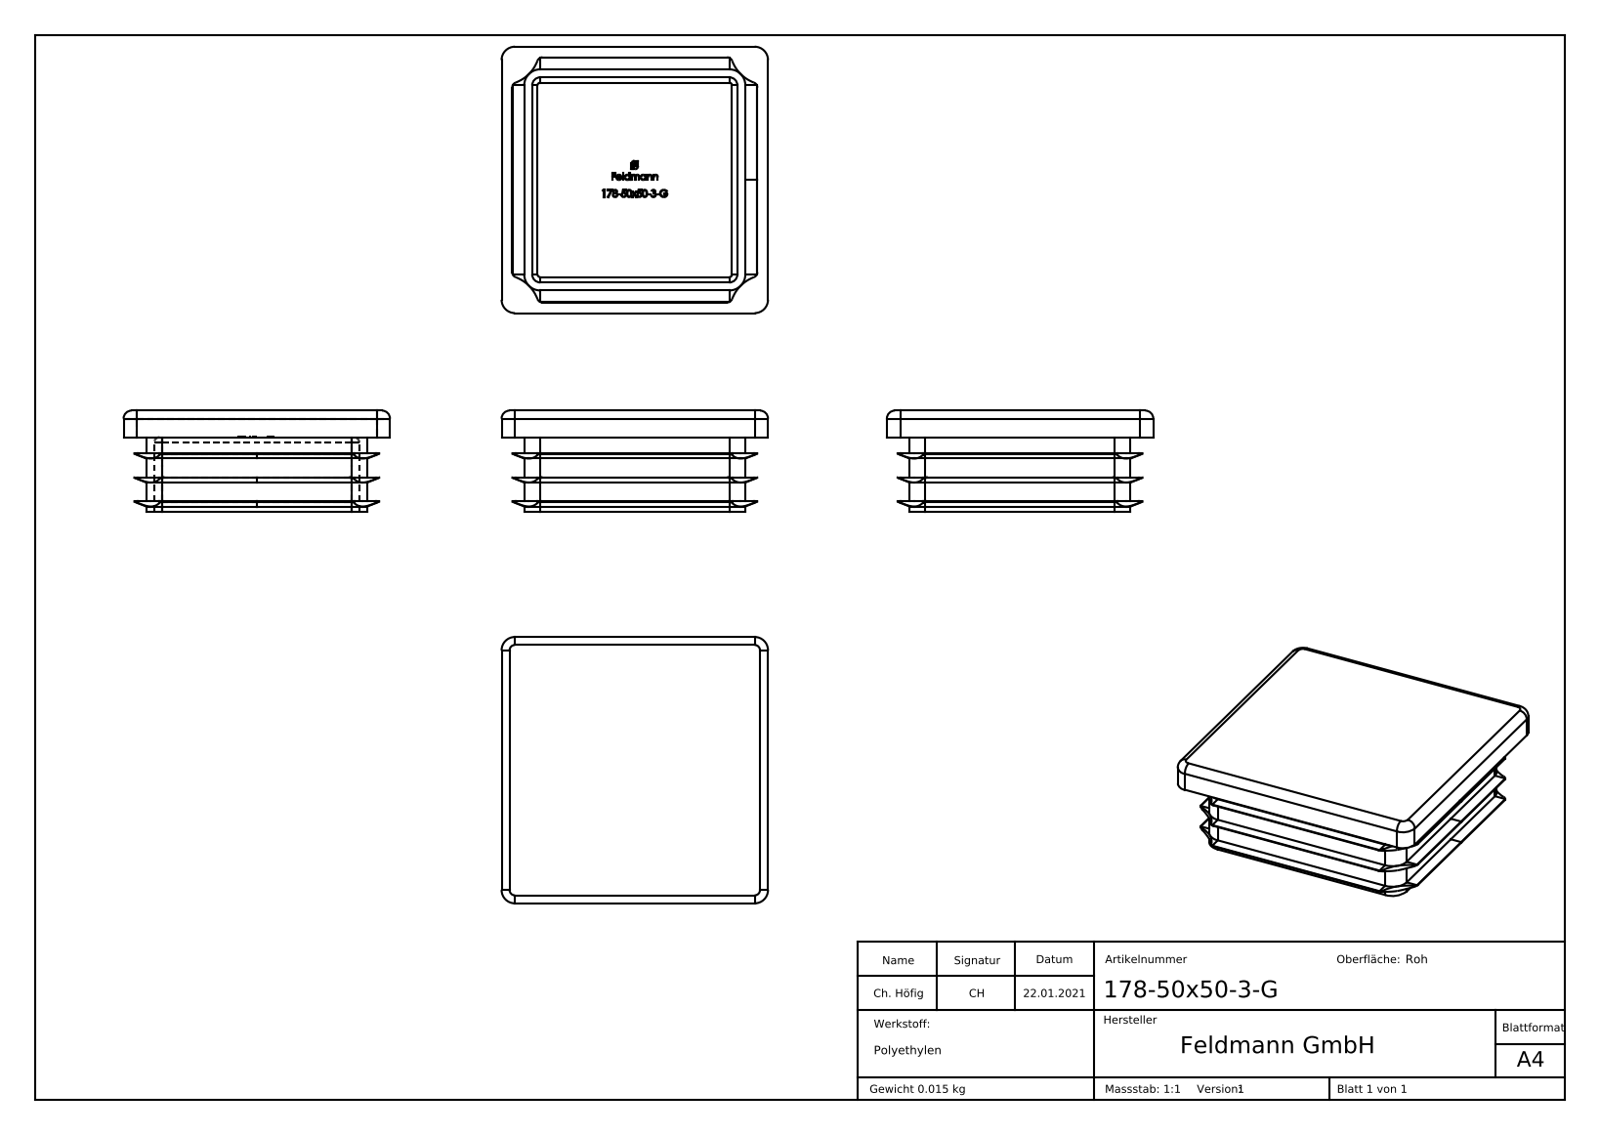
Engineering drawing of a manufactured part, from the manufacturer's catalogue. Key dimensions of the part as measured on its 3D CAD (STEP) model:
Part name (STEP PRODUCT): 178-50x50-3-G
STEP written by: SolidWorks 2018 (CONFIG_CONTROL_DESIGN)
Units: millimetres
Bodies: 1 solid, 497 faces (240 planar, 83 cylindrical, 174 other)
Overall size (bounding box): 50 × 50 × 19
Volume: 16 240 mm³ · Surface area: 11 845 mm²
Partial cylindrical surfaces — rounded edges, fillets, slot ends (radius × count): R1 ×12, R1.5 ×8, R2.5 ×4, R3 ×4, R7 ×4
Main face-to-face distances: 5, 1.5, 40, 38.5, 41.5, 4.5, 4.25, 5.75, 44.25, 45.75
